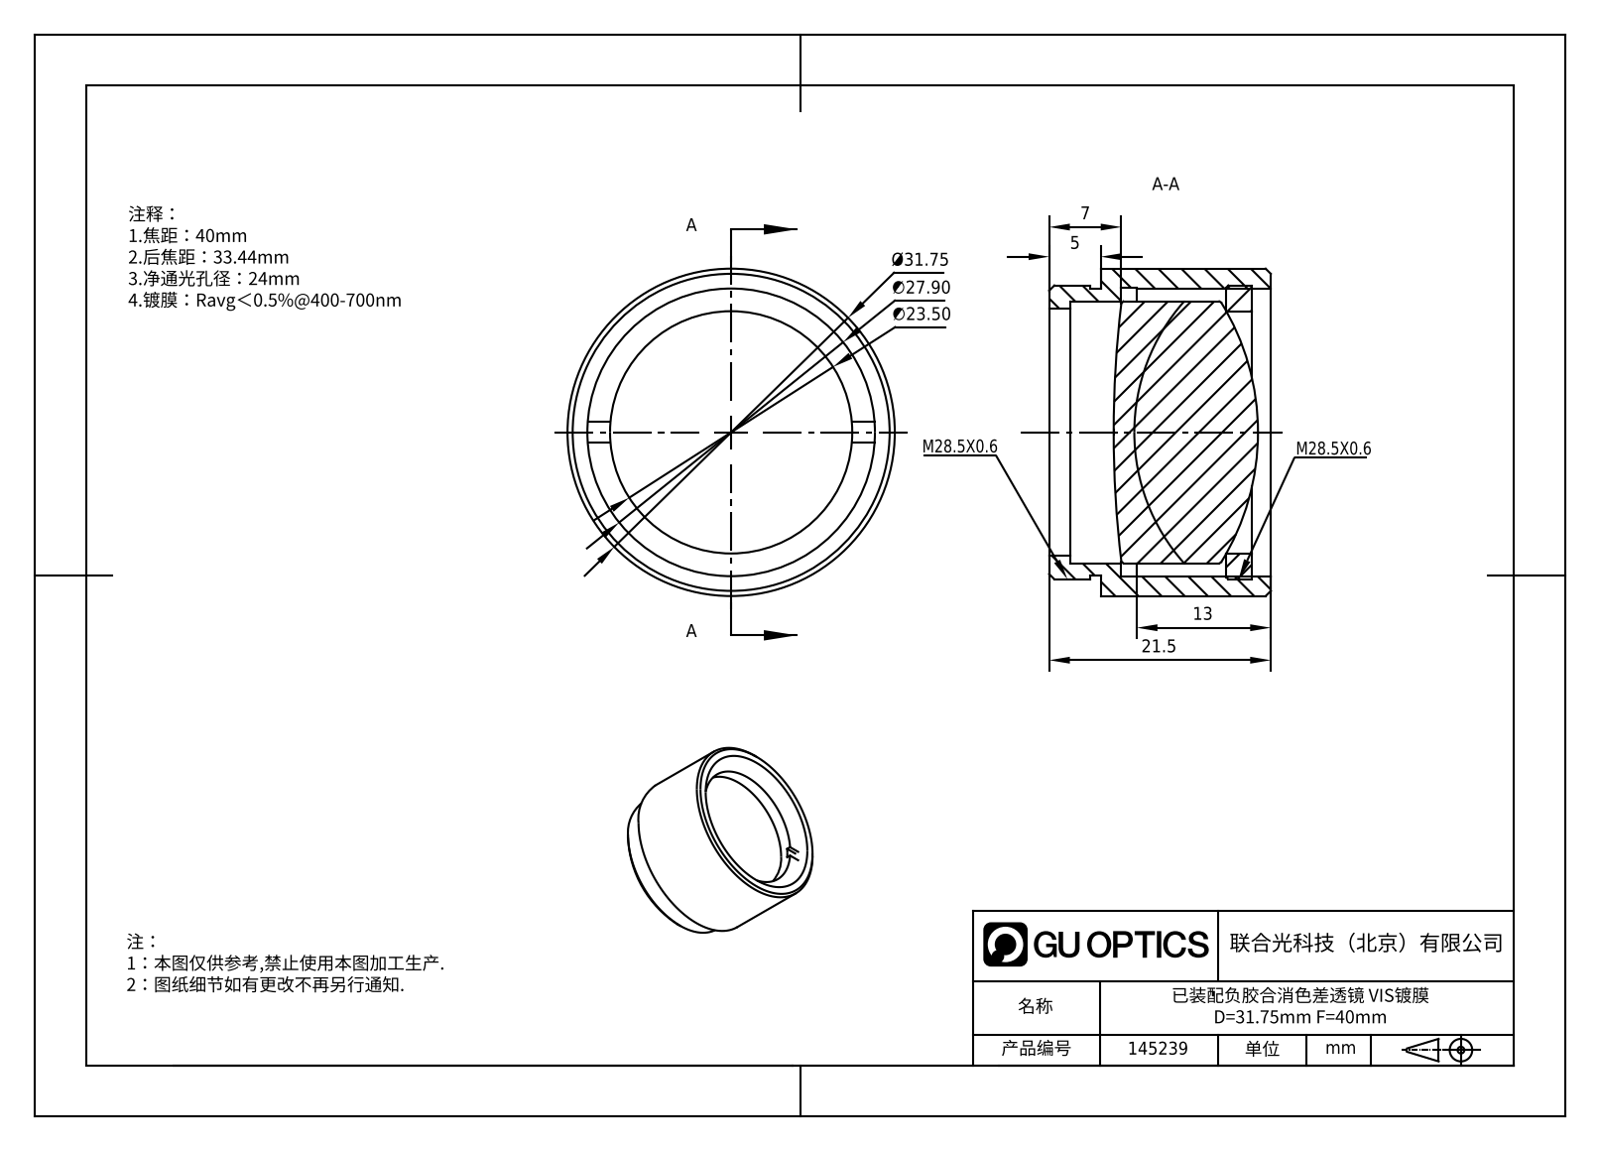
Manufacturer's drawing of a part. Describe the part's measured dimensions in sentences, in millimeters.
The part is named "APD-ML25-040-VIS; M28.5x0.6安装环PN35021-LM254-D2; M28.5x0.6ѹȦ; GL31-025B-040-VIS_Solidworks". Its 3-D file was written by "SolidWorks 2022 (AUTOMOTIVE_DESIGN)". It is 4 solids with 56 faces: 16 planar, 22 cylindrical and 18 other. Overall it measures 31.76 by 31.76 by 21.5 millimeters. Its volume is 9 463 cubic millimeters and its surface area 8 201 square millimeters. Round holes: 1 of diameter 23.5, 1 of diameter 24, 1 of diameter 27.9, 1 of diameter 28. Round bosses or shafts: 1 of diameter 31.76, 1 of diameter 28.5, 1 of diameter 27.8, 1 of diameter 25.4. The main face-to-face distances are 2, 5, 2.5, 10, 12.5, 17.5, 4, 15, 6.5, 21.5.
